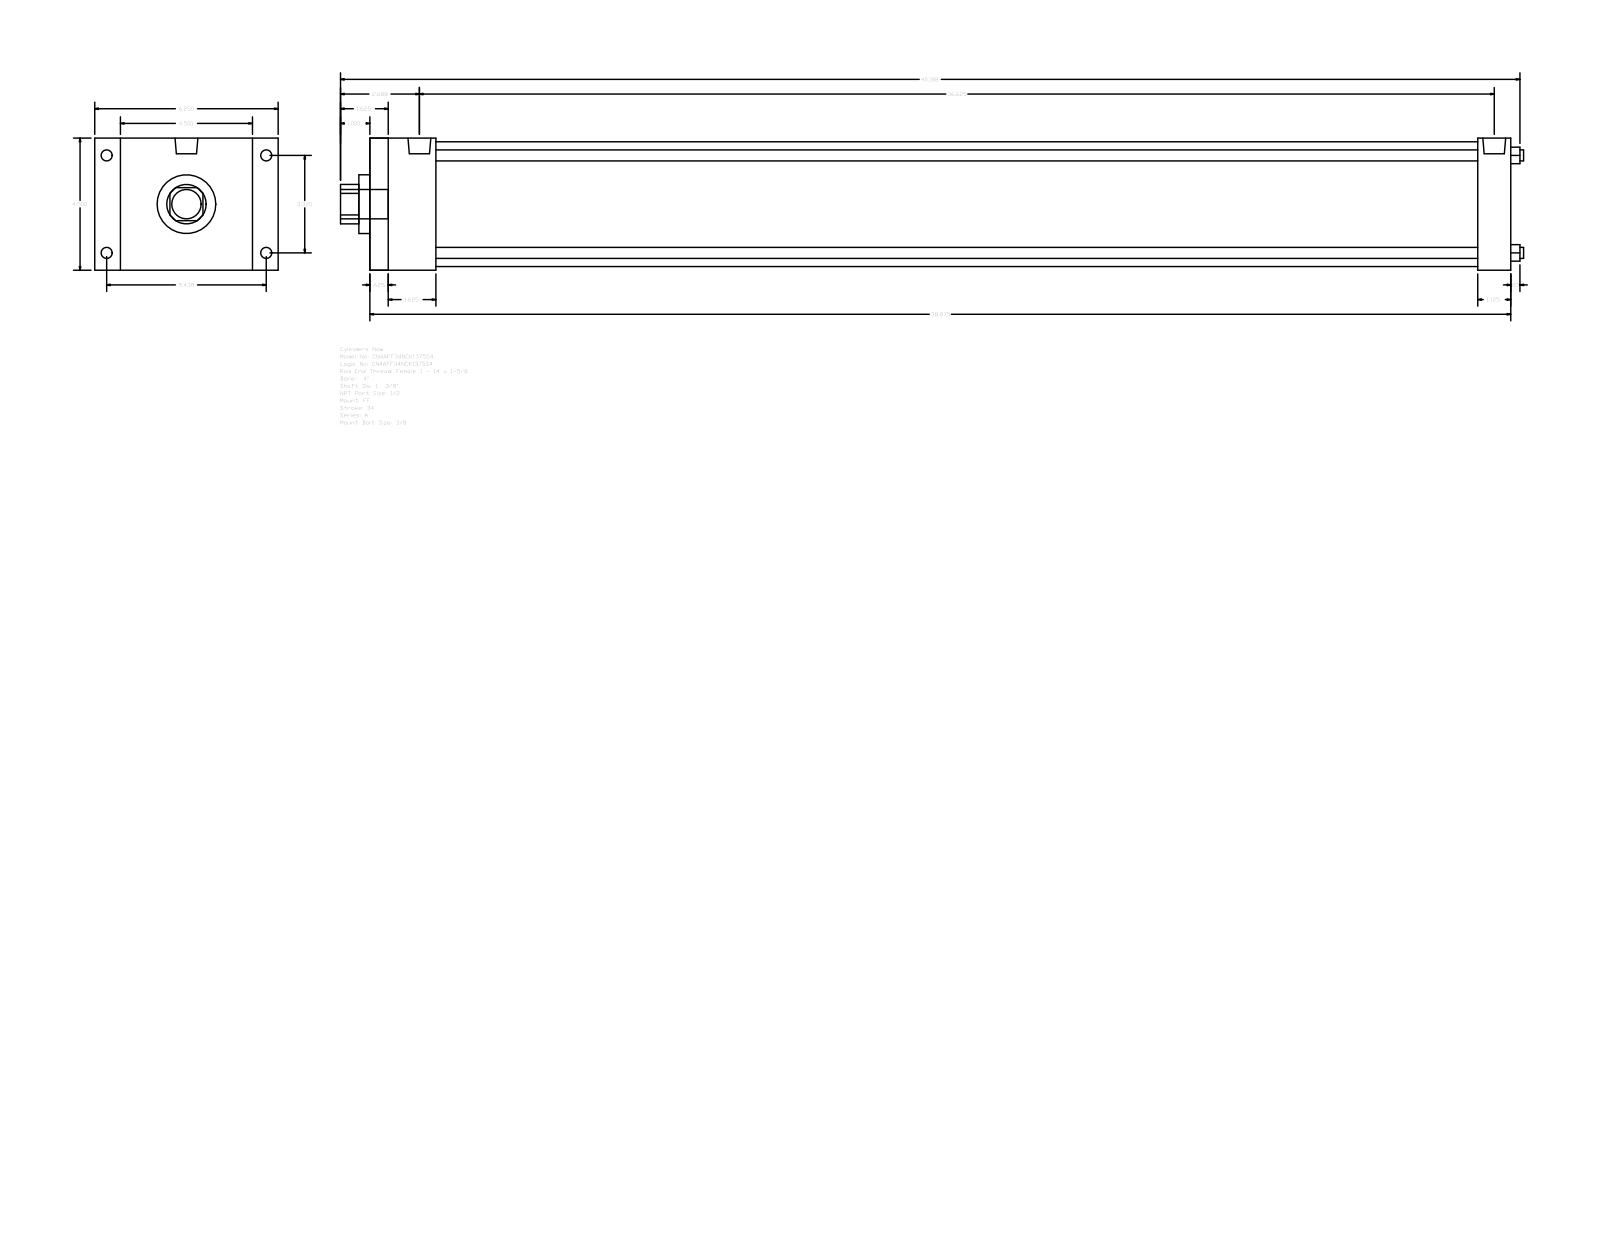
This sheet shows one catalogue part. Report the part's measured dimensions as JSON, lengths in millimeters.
{"part_name": "A_FF__0400_1.375", "step_written_by": "GSSL Pune (CONFIG_CONTROL_DESIGN)", "units": "millimeters", "bodies": {"solids": 0, "faces": 92, "planar": 64, "cylindrical": 28, "other": 0}, "overall_size": [1023.94, 158.75, 114.3], "round_holes": [[9.53, 4], [34.92, 1], [50.8, 1], [107.95, 1]], "round_bosses_or_shafts": [[9.53, 4], [8.73, 4], [19.77, 2], [25.4, 1]], "partial_cylinders_radius": [[17.06, 1]], "face_to_face_distances": [114.3, 987.43, 15.87, 971.56, 28.58, 22.23, 136.53, 958.85, 942.98, 57.15], "hole_center_spacings": [59.62, 84.32, 119.25]}
